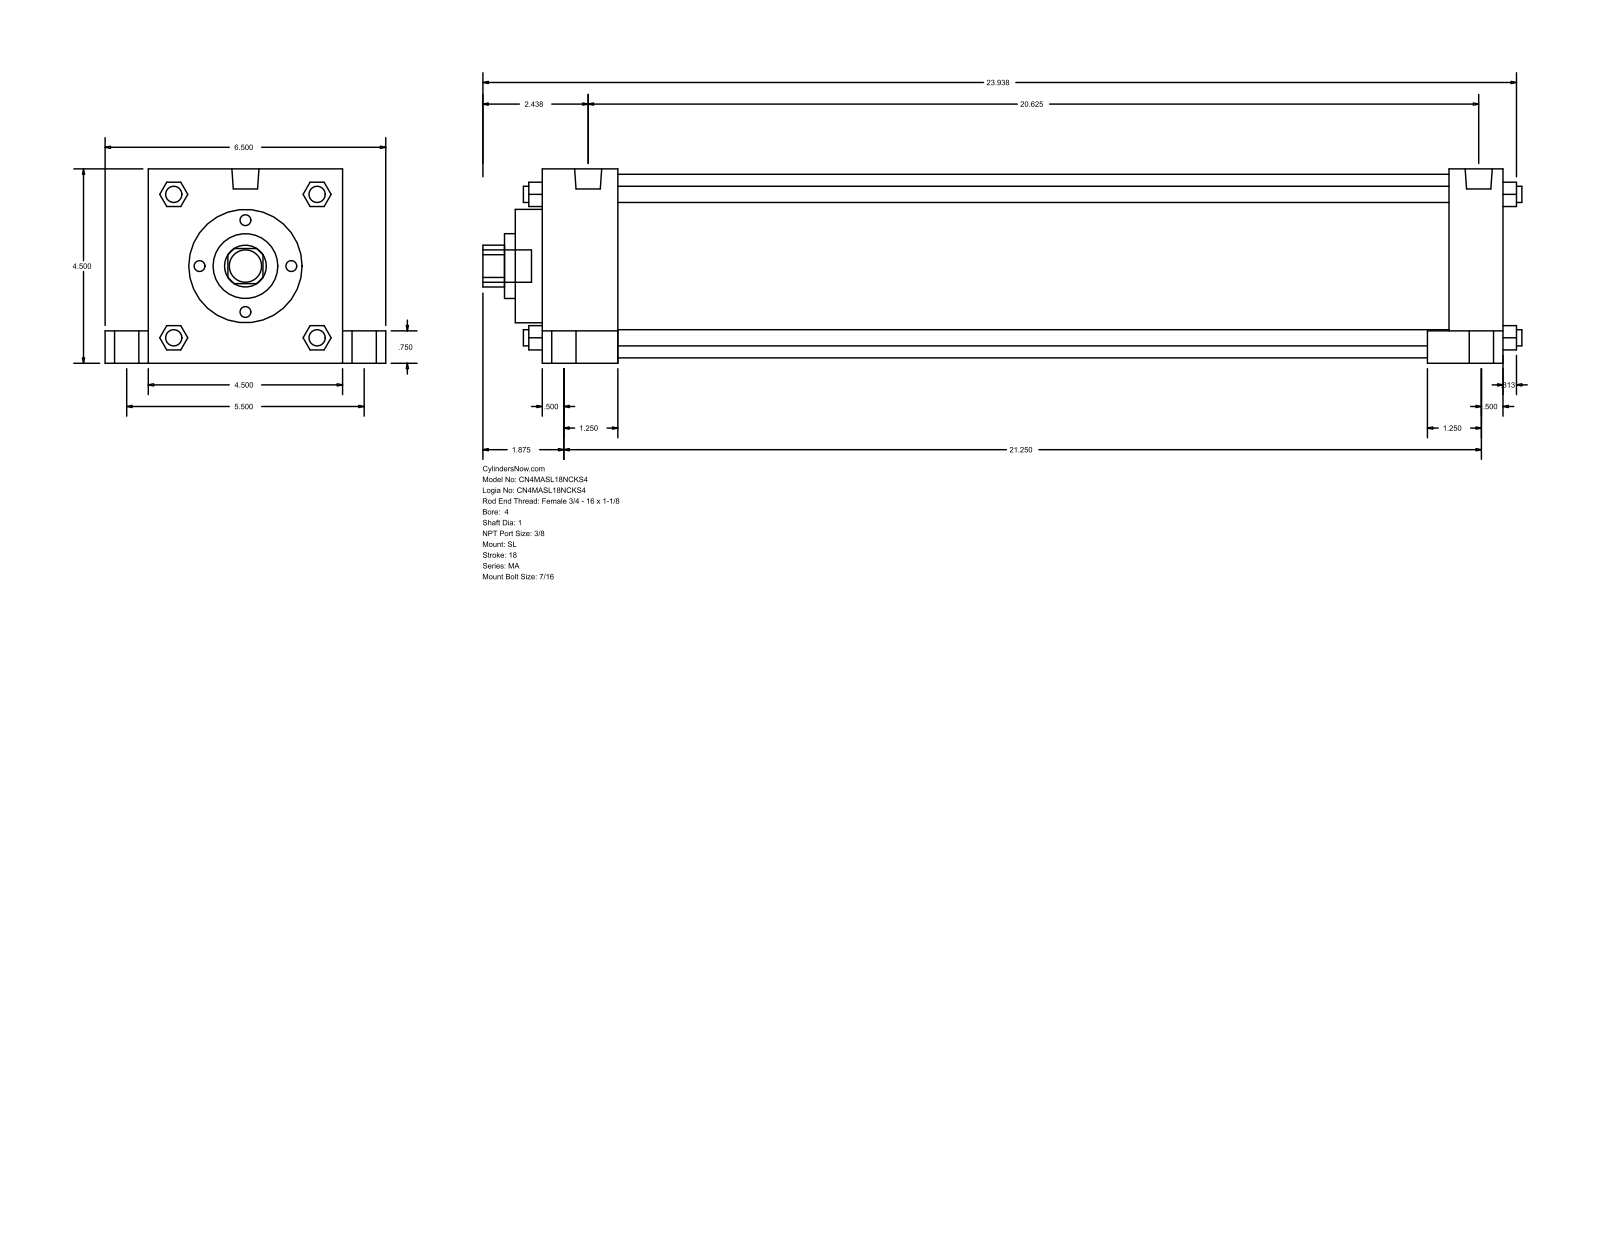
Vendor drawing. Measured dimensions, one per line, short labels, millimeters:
name: MA_SL__0400_1
written by: GSSL Pune (CONFIG_CONTROL_DESIGN)
unit: mm
bodies: 0 solids, 150 faces (113 planar, 37 cylindrical, 0 other)
size: 611.19 × 165.1 × 114.3
holes: 1× ⌀25.4, 1× ⌀38.1, 1× ⌀66.67, 1× ⌀107.95
bosses: 4× ⌀20.64, 4× ⌀14.29, 4× ⌀11.11, 4× ⌀9.53, 2× ⌀15.93, 1× ⌀19.05
rounds: 1× R12.29
face distances: 114.3, 565.16, 488.95, 44.46, 520.7, 533.41, 31.75, 25.4, 139.7, 19.05
